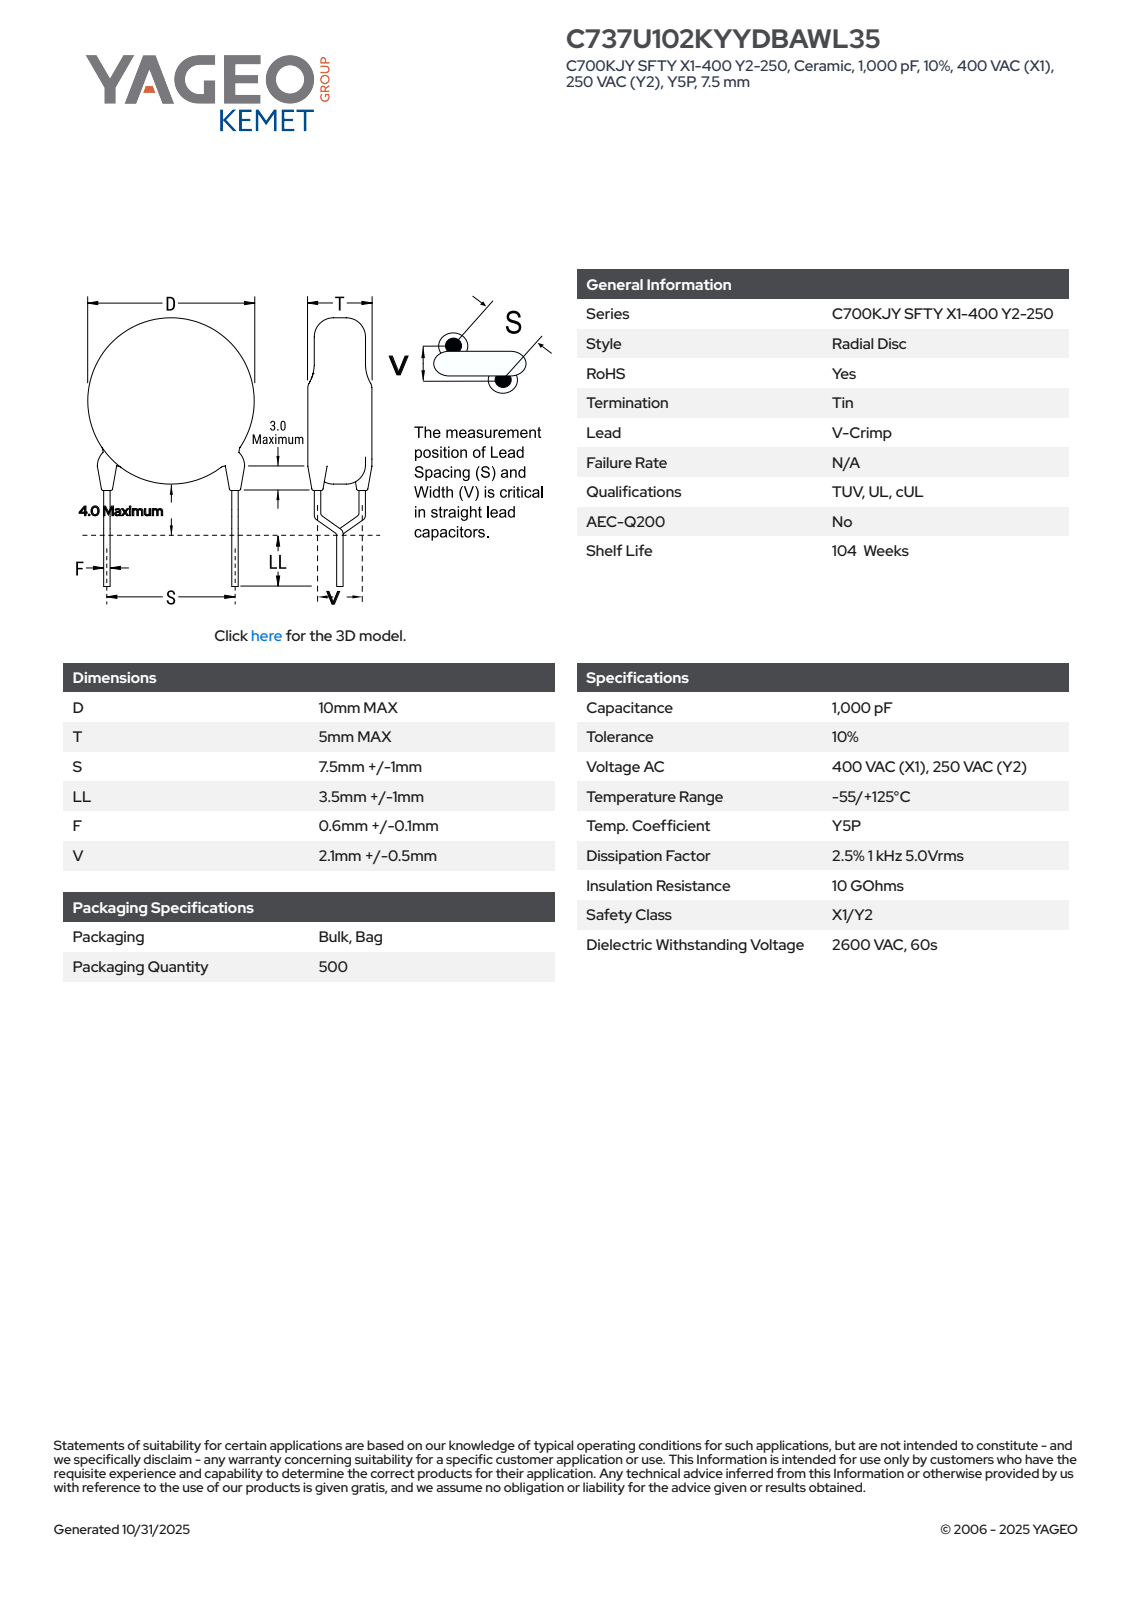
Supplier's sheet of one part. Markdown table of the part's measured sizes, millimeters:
| quantity | value |
| --- | --- |
| part name | CCD_VC10X5_D10T5S7.5LL4.5F0.7V2.1 |
| STEP written by | SolidWorks 2021 (AUTOMOTIVE_DESIGN) |
| units | millimeters |
| bodies | 4 solids, 88 faces (63 planar, 21 cylindrical, 4 other) |
| overall size | 14.5 × 10 × 5 |
| volume | 388 mm³ |
| surface area | 329 mm² |
| round bosses / shafts (diameter × count) | 0.7 × 6, 1.2 × 2, 10 × 1 |
| partial cylindrical surfaces (radius × count) | 0.6 × 2 |
| main face-to-face distances | 5, 4.5, 10.29, 5.79, 9.08, 4.58, 1.21, 0.33, 0.98, 4.95 |
